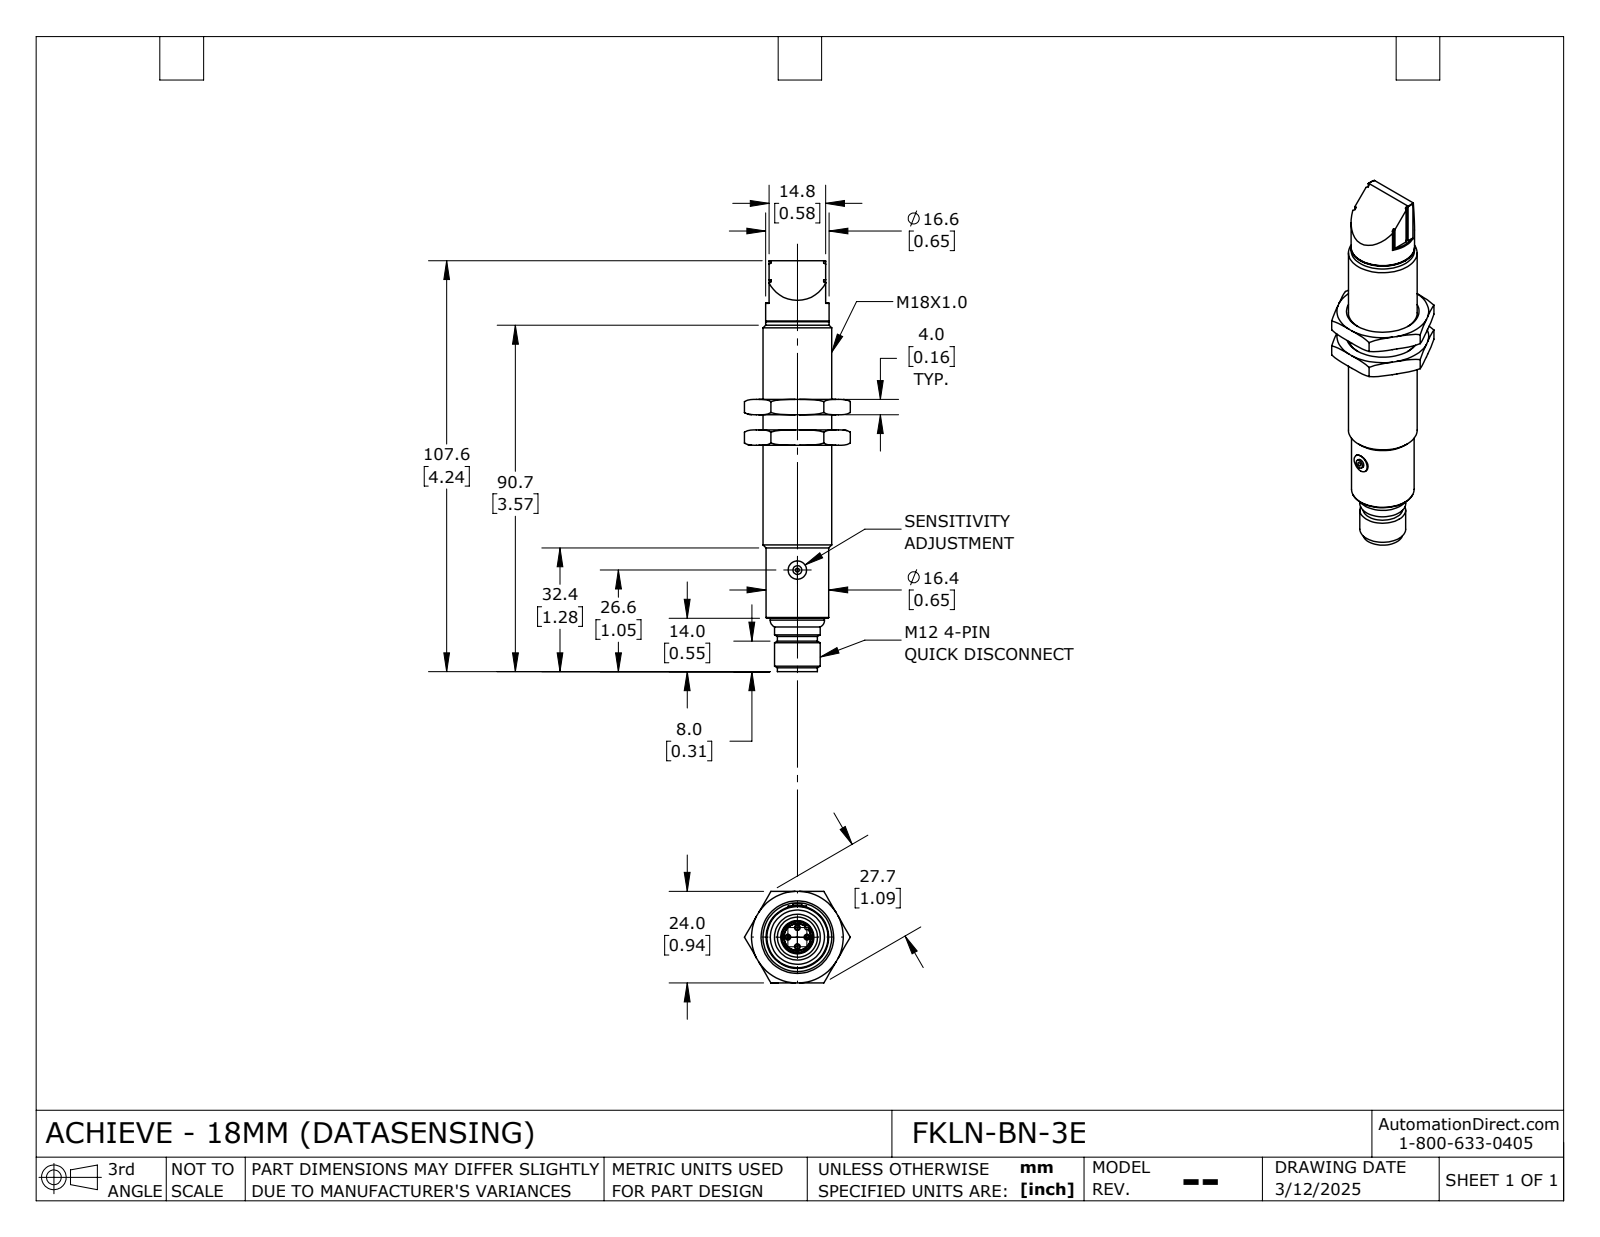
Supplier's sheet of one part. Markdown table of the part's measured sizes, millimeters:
| quantity | value |
| --- | --- |
| part name | FKLN-BN-3E_Default |
| STEP written by | SolidWorks 2024 (CONFIG_CONTROL_DESIGN) |
| units | millimeters |
| bodies | 3 solids, 146 faces (64 planar, 30 cylindrical, 52 other) |
| overall size | 107.6 × 27.7 × 24 |
| volume | 24 120 mm³ |
| surface area | 9 064 mm² |
| round holes (diameter × count) | 4.7 × 1, 7.1 × 1, 8.3 × 1, 14.8 × 1, 18 × 1 |
| round bosses / shafts (diameter × count) | 1 × 4, 16.6 × 1, 16.4 × 1, 14.2 × 1, 12 × 1, 10.5 × 1, 7 × 1, 4.8 × 1 |
| partial cylindrical surfaces (radius × count) | 0.1 × 2, 0.5 × 2, 0.6 × 1, 7.5 × 1 |
| main face-to-face distances | 4, 8, 24, 31.8, 32, 23.8, 24, 12, 35.8, 36 |
